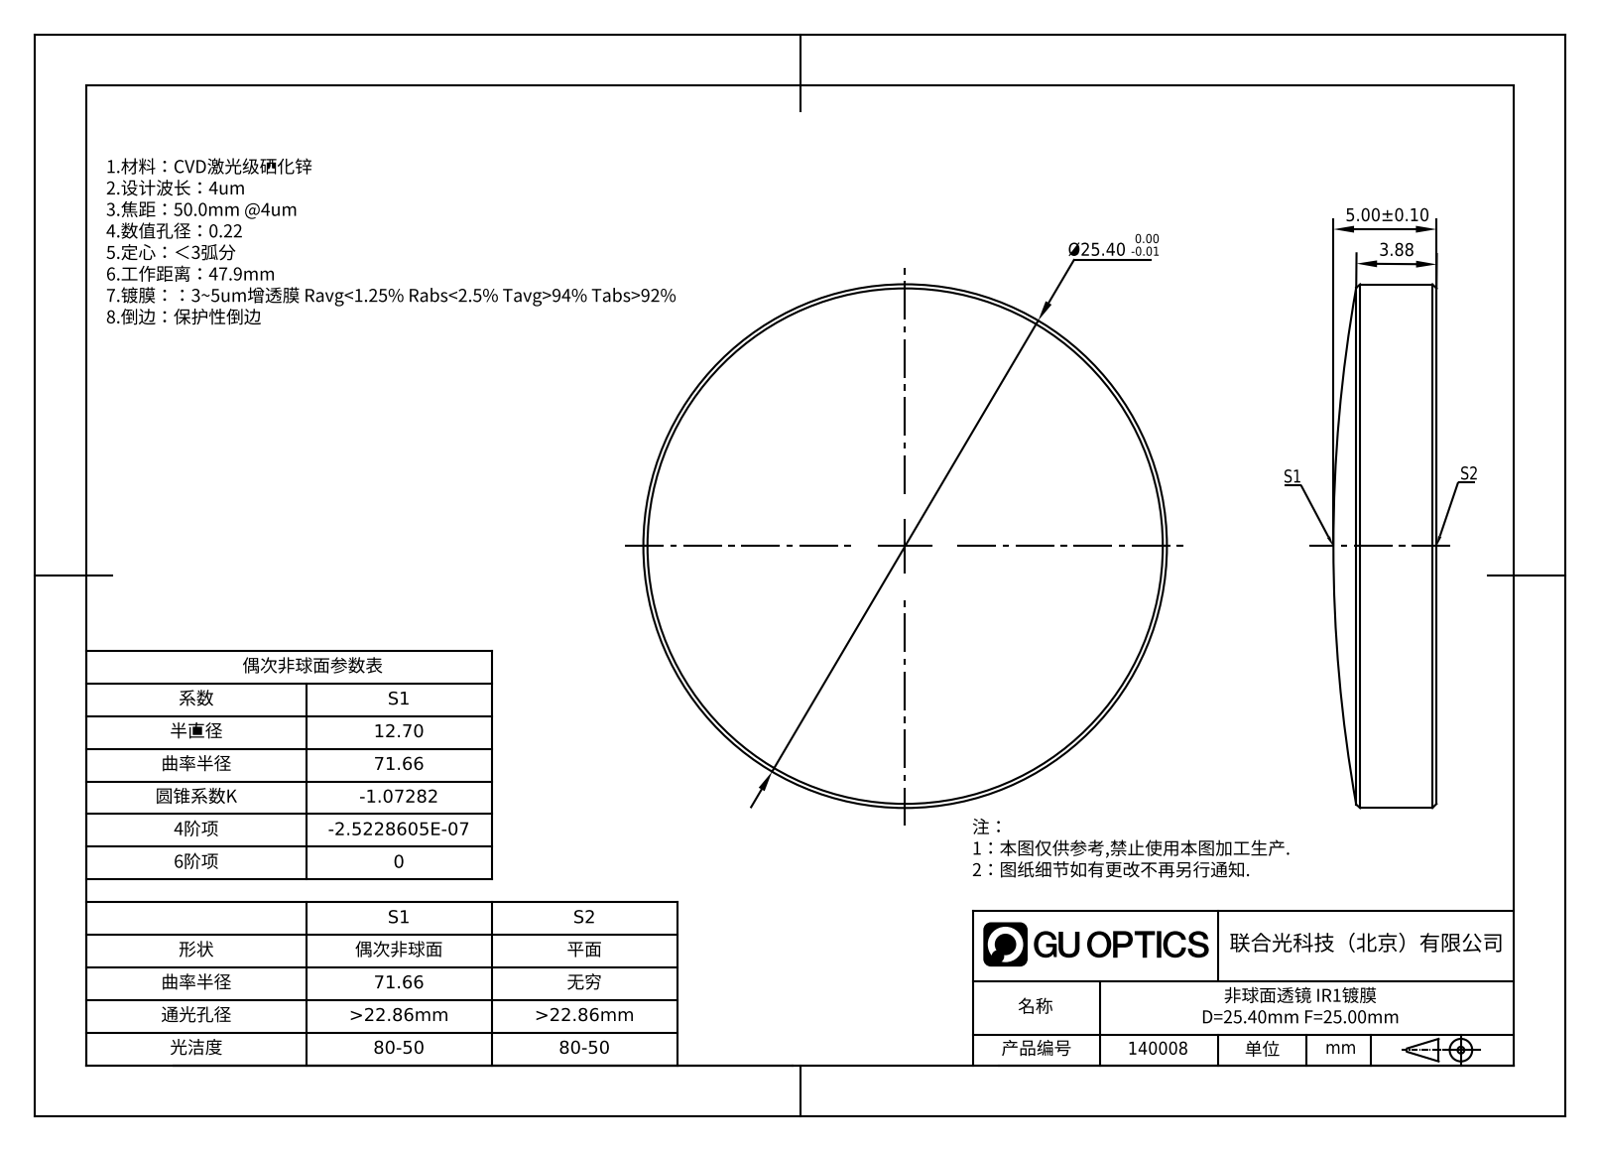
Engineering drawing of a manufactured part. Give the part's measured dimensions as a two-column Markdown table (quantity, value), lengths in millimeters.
| quantity | value |
| --- | --- |
| part name | GL7AL1-025-050-IR1 |
| STEP written by | SolidWorks 2022 (AUTOMOTIVE_DESIGN) |
| units | millimeters |
| bodies | 1 solid, 9 faces (1 planar, 2 cylindrical, 6 other) |
| overall size | 25.4 × 25.4 × 5 |
| volume | 2 244 mm³ |
| surface area | 1 310 mm² |
| round bosses / shafts (diameter × count) | 25.4 × 1 |
